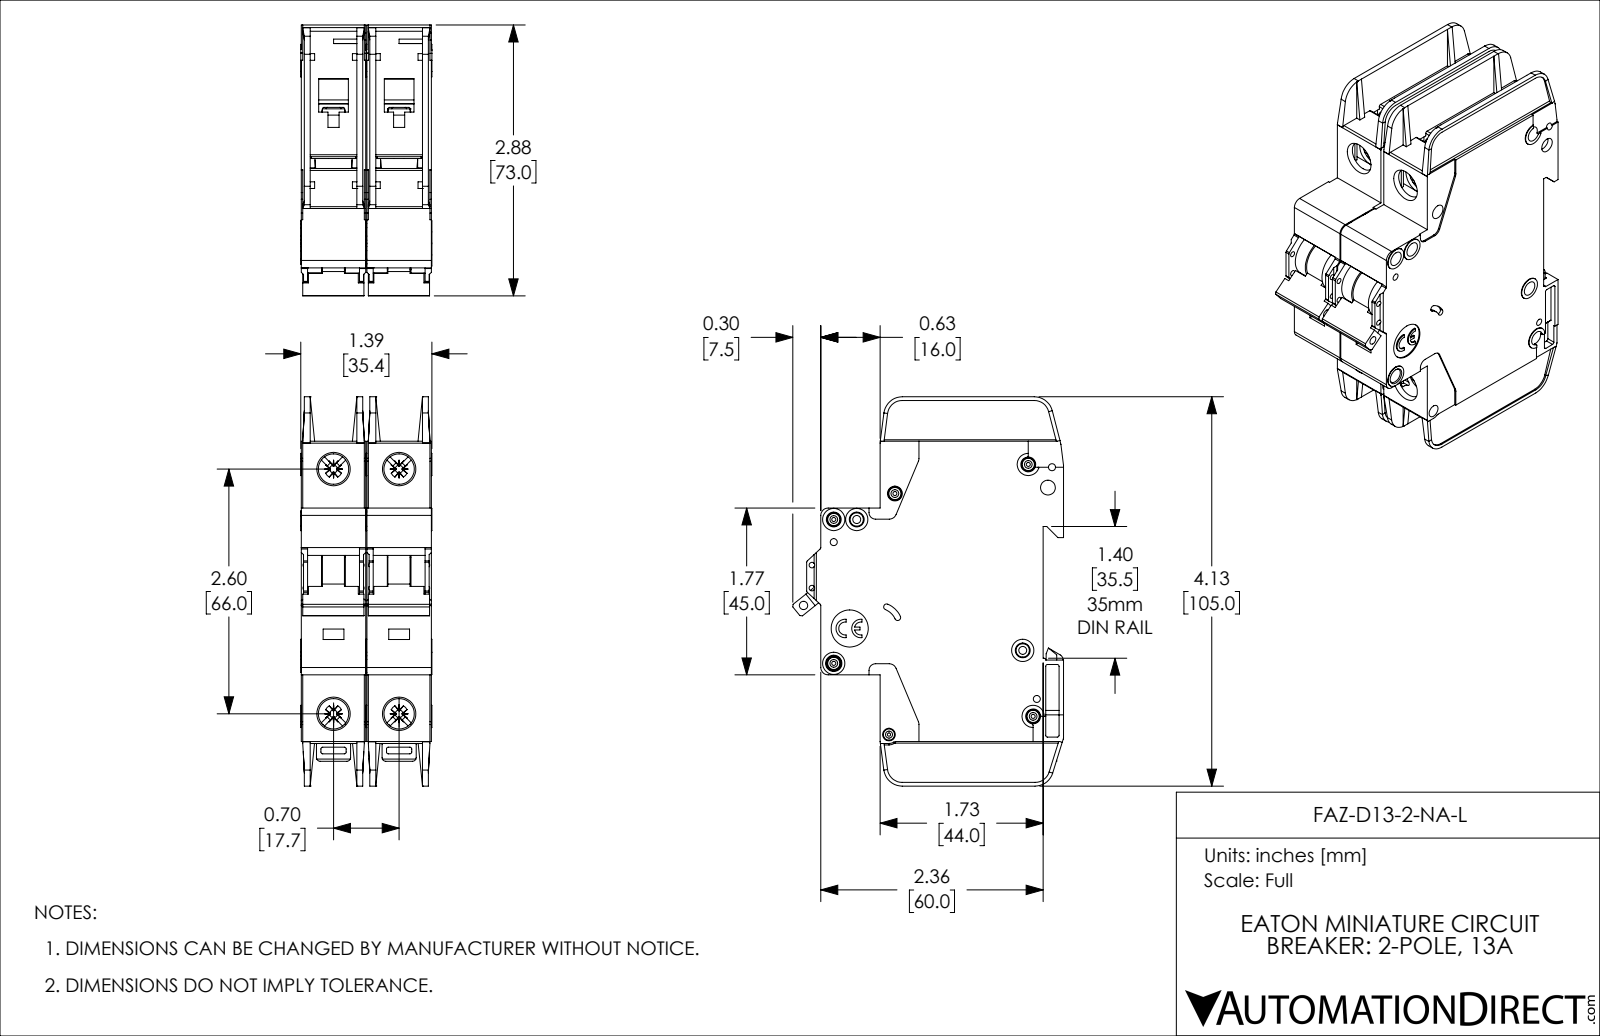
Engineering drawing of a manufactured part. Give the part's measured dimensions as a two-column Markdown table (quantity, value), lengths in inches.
| quantity | value |
| --- | --- |
| part name | FAZ-D13-2-NA-L |
| STEP written by | SolidWorks 2019 (AUTOMOTIVE_DESIGN) |
| units | inches |
| bodies | 2 solids, 2254 faces (1342 planar, 714 cylindrical, 198 other) |
| overall size | 4.134 × 2.876 × 1.394 |
| volume | 9.365 in³ |
| surface area | 82.01 in² |
| round holes (diameter × count) | 0.157 × 8, 0.043 × 5, 0.075 × 4, 0.323 × 4, 0.059 × 2, 0.085 × 2, 0.035 × 1, 0.089 × 1, 0.098 × 1, 0.134 × 1, 0.394 × 1 |
| round bosses / shafts (diameter × count) | 0.13 × 5, 0.236 × 4, 0.118 × 3, 0.098 × 2 |
| partial cylindrical surfaces (radius × count) | 0.02 × 57, 0.016 × 20, 0.039 × 14, 0.079 × 10, 0.043 × 8, 0.008 × 5, 0.197 × 5, 0.01 × 4 |
| main face-to-face distances | 0.697, 0.047, 0.685, 0.591, 0.094, 0.638, 0.543, 1.382, 0.744, 0.65 |
| hole center spacings | 0.244, 0.537, 0.697, 0.87, 2.598, 2.69, 0.189, 0.199 |
